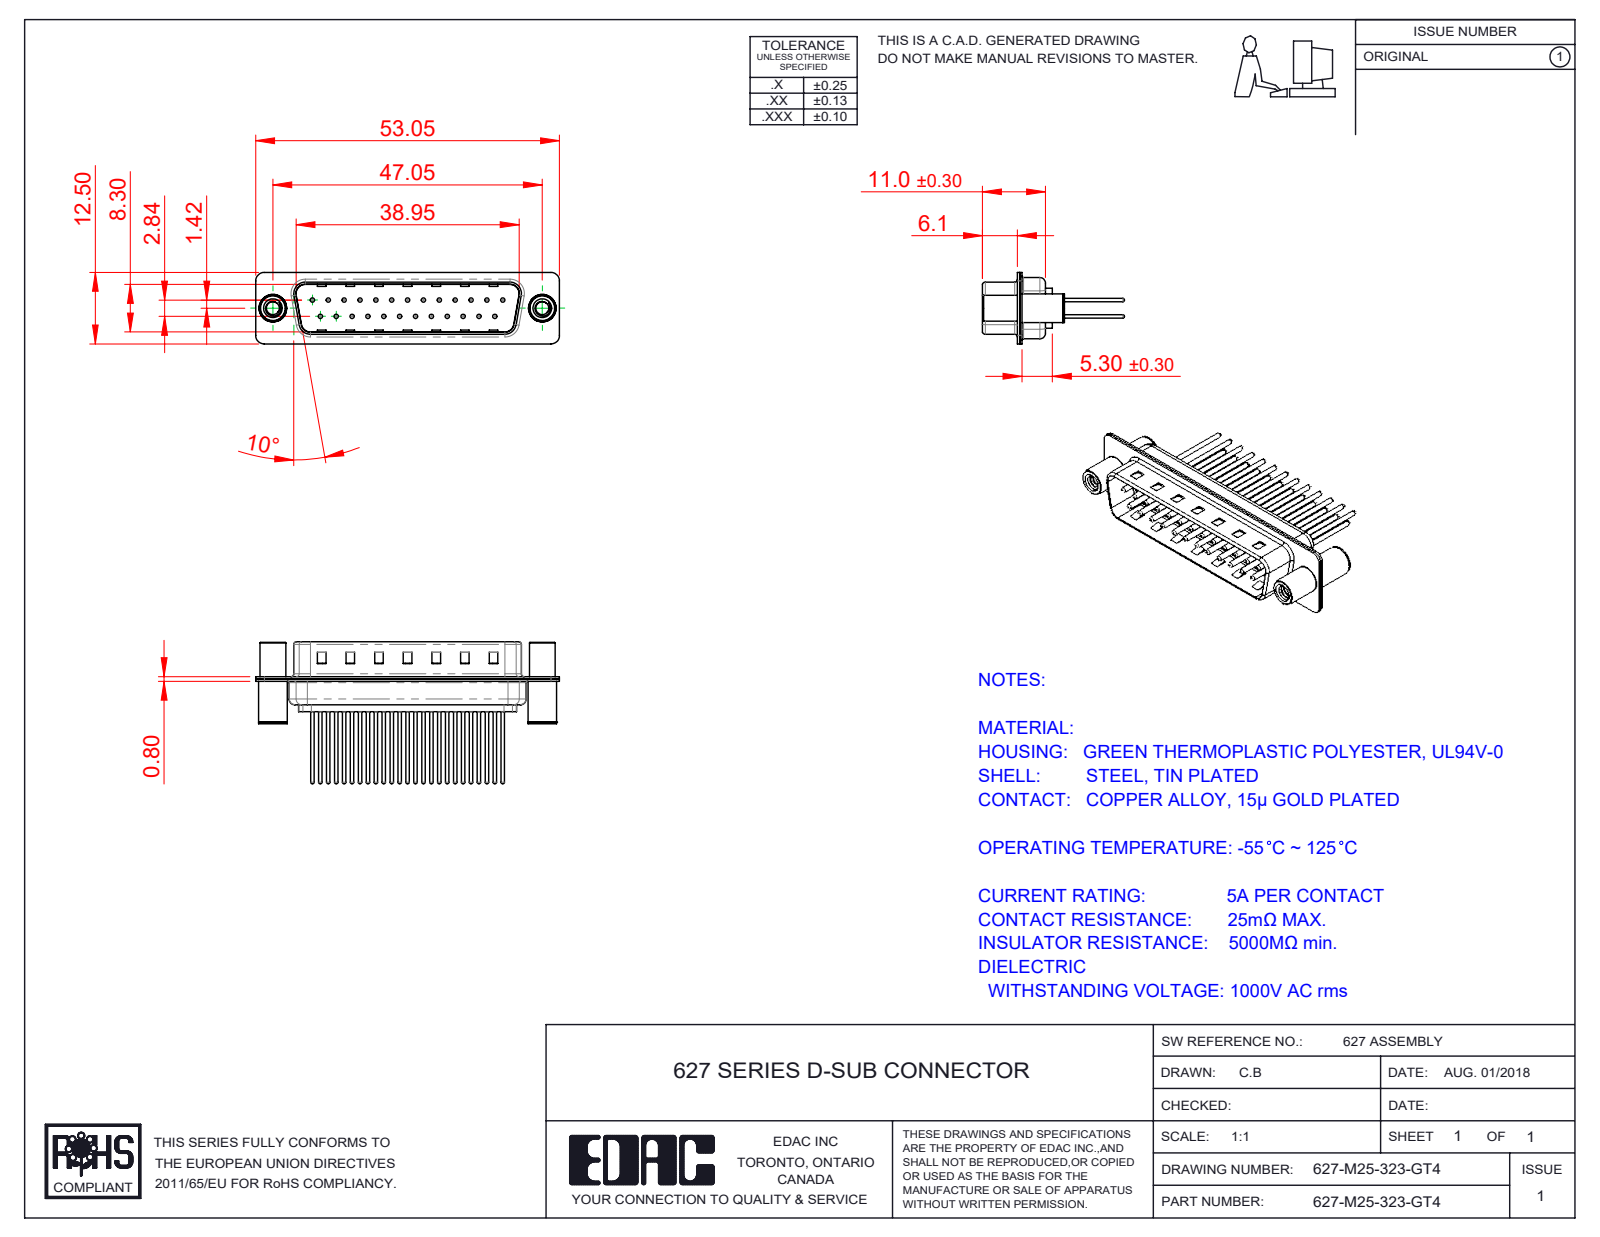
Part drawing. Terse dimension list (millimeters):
name: 627M Shell Front_25 Contacts; 627-M25-323-GT4; 627M 4-40 Threaded Standoff and Board Spacer; 627M Contact Row 2_23 (+3 more)
written by: SolidWorks 2020 (CONFIG_CONTROL_DESIGN)
unit: mm
bodies: 30 solids, 1387 faces (352 planar, 539 cylindrical, 496 other)
size: 53.05 × 24.77 × 12.5
volume: 3 055 mm³; area: 7 696 mm²
holes: 25× ⌀0.75, 25× ⌀1.6, 25× ⌀2, 2× ⌀2.26, 2× ⌀3.26, 2× ⌀4, 2× ⌀4.8
bosses: 25× ⌀1.5, 25× ⌀0.6, 2× ⌀5, 2× ⌀4.9, 2× ⌀4.5
rounds: 16× R1.5, 12× R2, 8× R0.5, 8× R1.6, 4× R0.25, 4× R0.6, 4× R0.65, 4× R0.9
face distances: 0.4, 0.8, 9.5, 9.1, 8.7, 9.9, 1.2, 5.7, 6.1, 0.75
hole spacings: 3.16, 2.77, 5.54, 8.31, 11.08, 13.85, 16.62, 5.03
